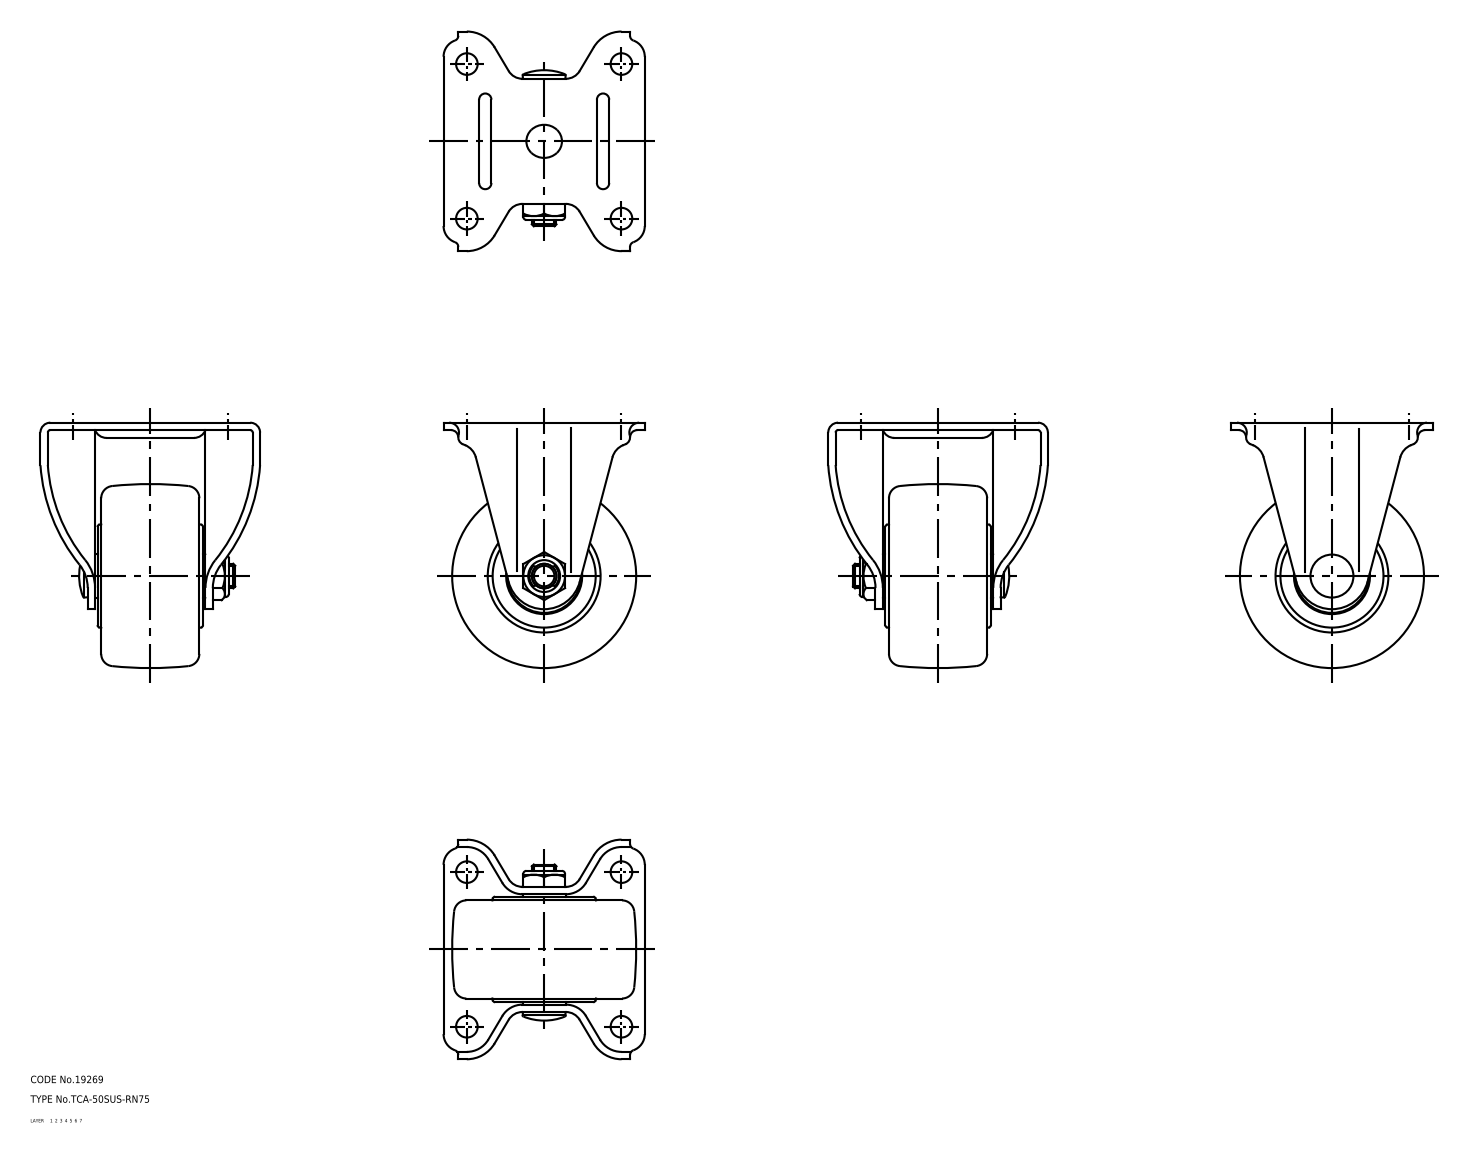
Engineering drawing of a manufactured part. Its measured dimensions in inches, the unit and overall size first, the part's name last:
Units: inches
Overall size (bounding box): 3.937 × 3.524 × 3.228
Volume: 13.27 in³ · Surface area: 79.4 in²
Bodies: 4 solids, 253 faces (0 planar, 0 cylindrical, 253 other)
Part name (STEP PRODUCT): 67123708; 67123721; 67123734; 67123747
STEP written by: CADfix (AUTOMOTIVE_DESIGN)
